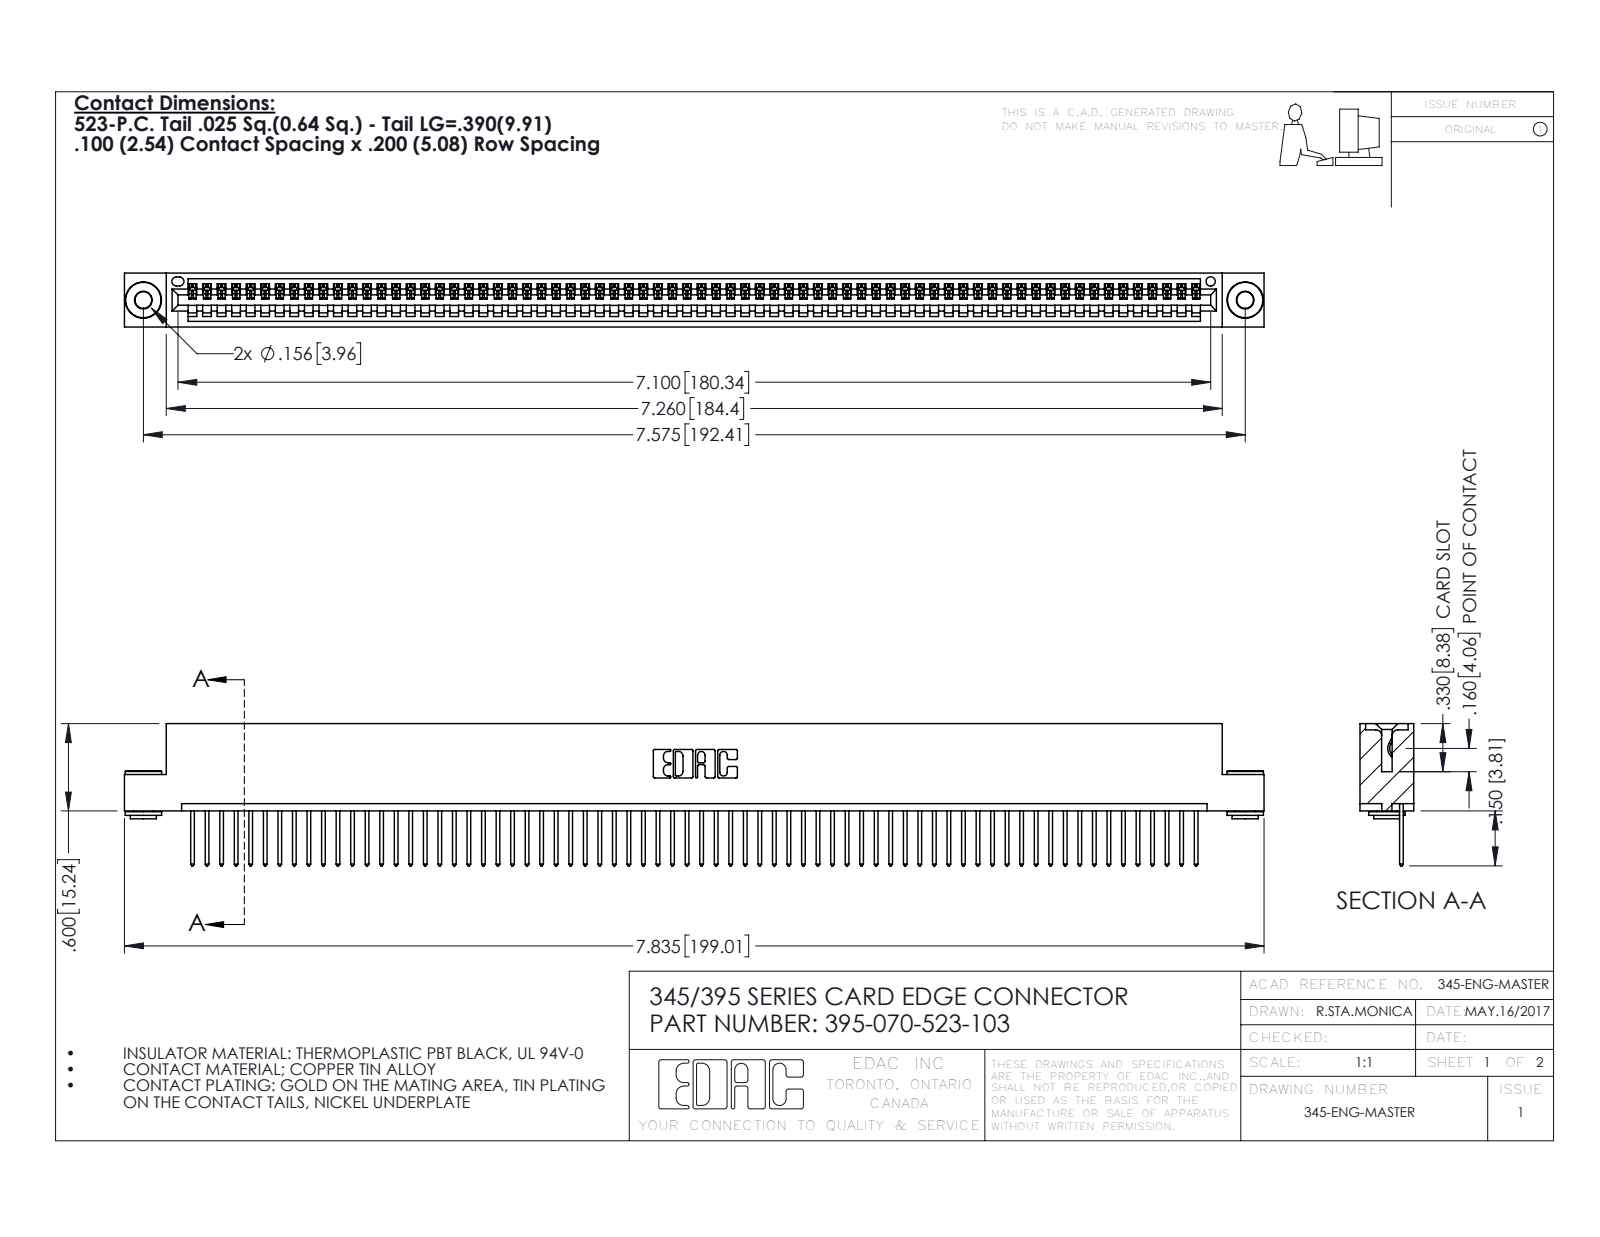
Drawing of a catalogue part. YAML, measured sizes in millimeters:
part_name: "395-070-523-103; 345-250-002_345-250-002-102; 345-292-001_345-293-123; 345 Part_Flush Mounting Lugs - 0.156 Dia-TH"
step_written_by: "SolidWorks 2016 (CONFIG_CONTROL_DESIGN)"
units: millimeters
bodies: {solids: 73, faces: 4224, planar: 2890, cylindrical: 1326, other: 8}
overall_size: [199, 24.8, 9.4]
volume: 19120
surface_area: 26080
round_holes:
  - {diameter: 2.9, count: 2}
  - {diameter: 4, count: 2}
  - {diameter: 1.6, count: 1}
round_bosses_or_shafts:
  - {diameter: 6.4, count: 2}
  - {diameter: 4.6, count: 2}
  - {diameter: 3.5, count: 2}
partial_cylinders:
  - {radius: 0.2, count: 140}
  - {radius: 0.3, count: 140}
  - {radius: 0.3, count: 22}
  - {radius: 0.2, count: 6}
  - {radius: 0.8, count: 6}
  - {radius: 0.7, count: 3}
  - {radius: 0.8, count: 2}
  - {radius: 1, count: 2}
face_to_face_distances: [1.8, 7.6, 9.4, 5.1, 0.6, 2.5, 6.9, 5.7, 3.8, 1.8]
hole_center_spacings: [6.9, 186.4, 192.4]
